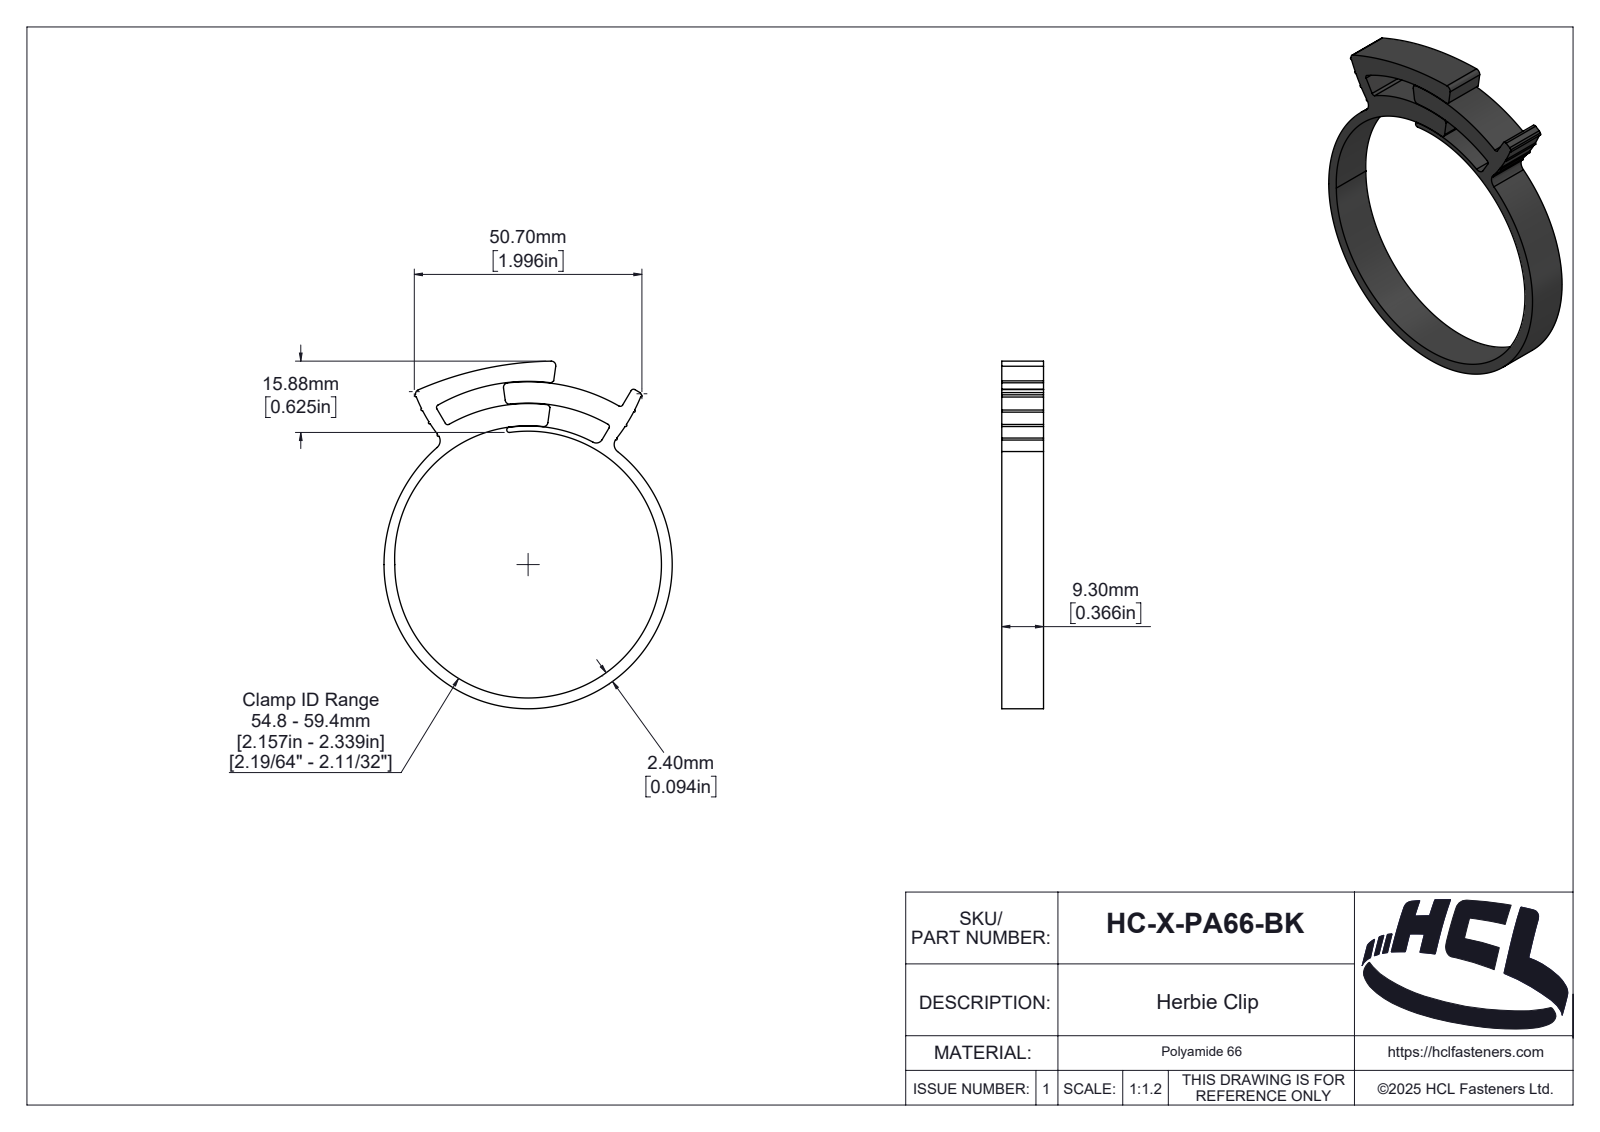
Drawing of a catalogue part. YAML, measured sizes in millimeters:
part_name: "HC-X-PA66-BK"
step_written_by: "SolidWorks 2025 (AUTOMOTIVE_DESIGN)"
units: millimeters
bodies: {solids: 1, faces: 162, planar: 13, cylindrical: 100, other: 49}
overall_size: [77.39, 64.2, 9.3]
volume: 7766
surface_area: 6993
partial_cylinders:
  - {radius: 0.25, count: 8}
  - {radius: 0.6, count: 6}
  - {radius: 1, count: 5}
  - {radius: 2, count: 2}
  - {radius: 0.17, count: 1}
  - {radius: 0.57, count: 1}
  - {radius: 0.67, count: 1}
  - {radius: 0.84, count: 1}
face_to_face_distances: [9.3]
